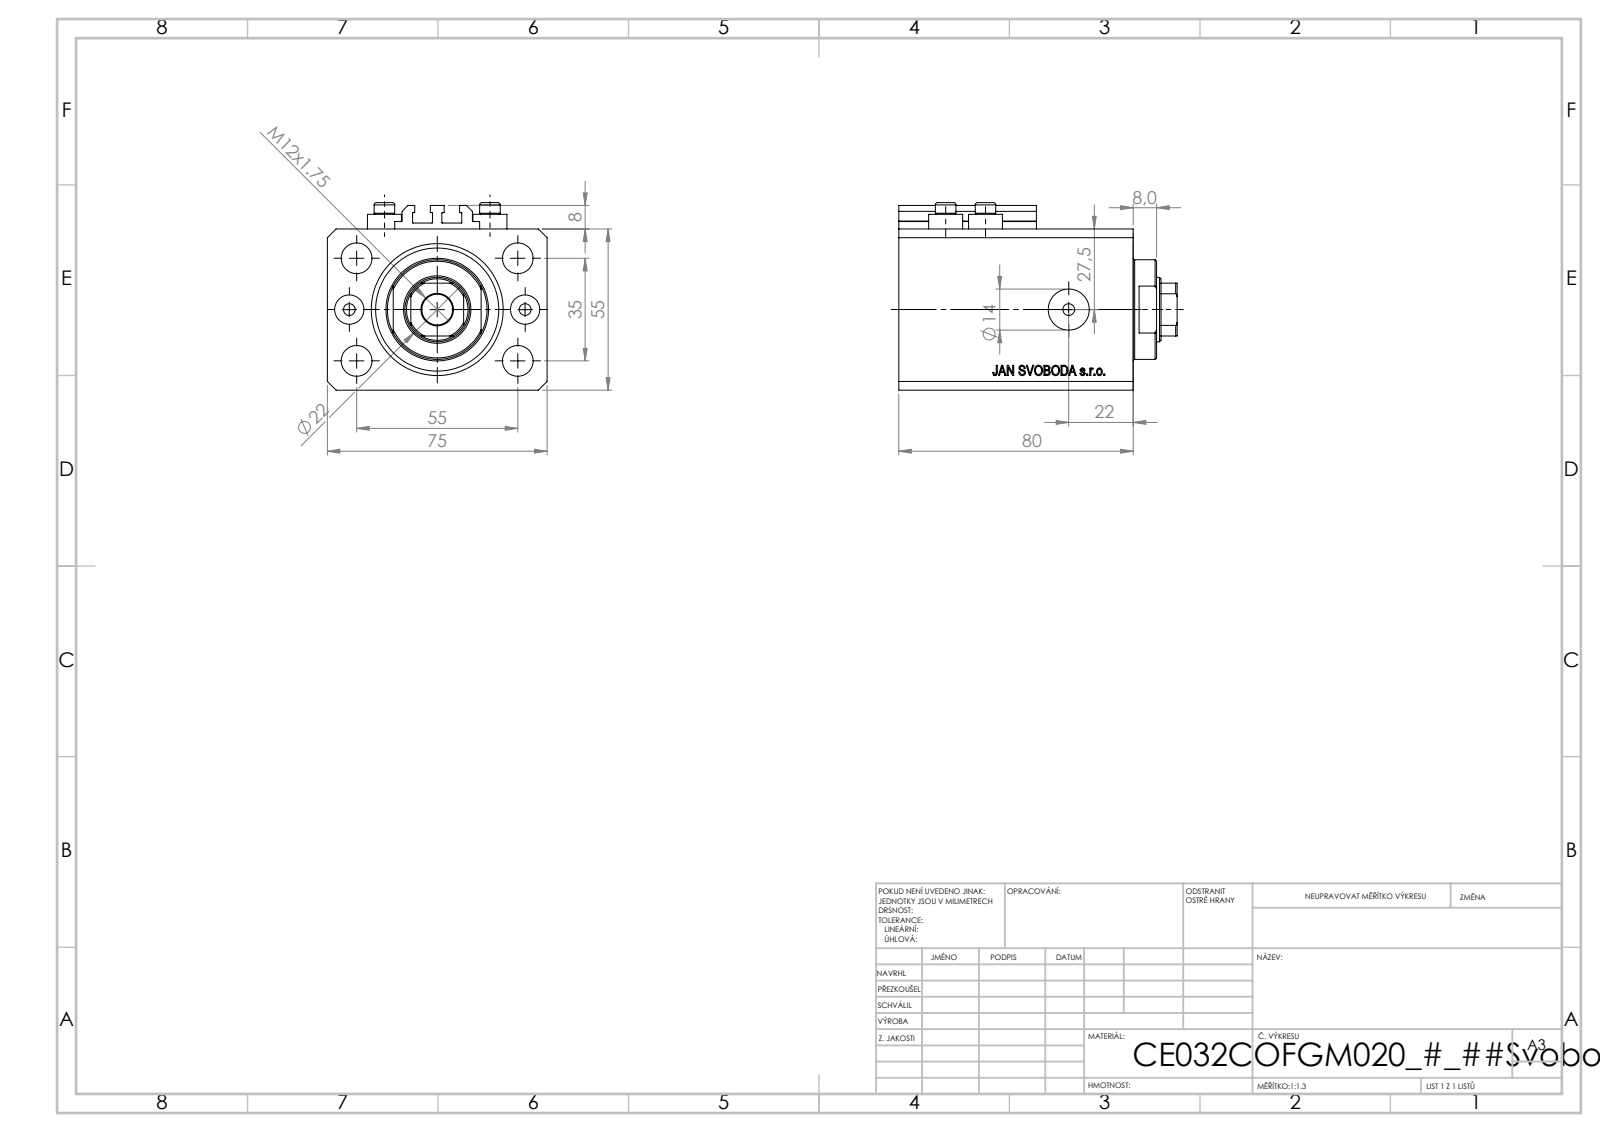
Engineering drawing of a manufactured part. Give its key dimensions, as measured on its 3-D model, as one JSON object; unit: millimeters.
{"part_name": "V250CE_VC_C; V250CE_C_VCP; ALLEN BOLT V250CE; V250CE_C_Body", "step_written_by": "SolidWorks 2019 (CONFIG_CONTROL_DESIGN)", "units": "millimeters", "bodies": {"solids": 8, "faces": 1034, "planar": 504, "cylindrical": 86, "other": 444}, "overall_size": [95, 75, 64], "volume_mm3": 305050, "surface_area_mm2": 71456, "round_holes": [[4, 8], [10.5, 5], [10, 2], [14, 2], [22, 1], [32, 1], [45, 1]], "round_bosses_or_shafts": [[11.6, 4], [7, 4], [34, 1]], "partial_cylinders_radius": [[0.2, 10], [10.5, 1]], "face_to_face_distances": [55, 75, 80, 15, 65, 9.9, 55.1, 70.1, 3, 8], "hole_center_spacings": [17.68, 32.6, 60.1, 36, 13.6, 30, 35, 38.48]}
